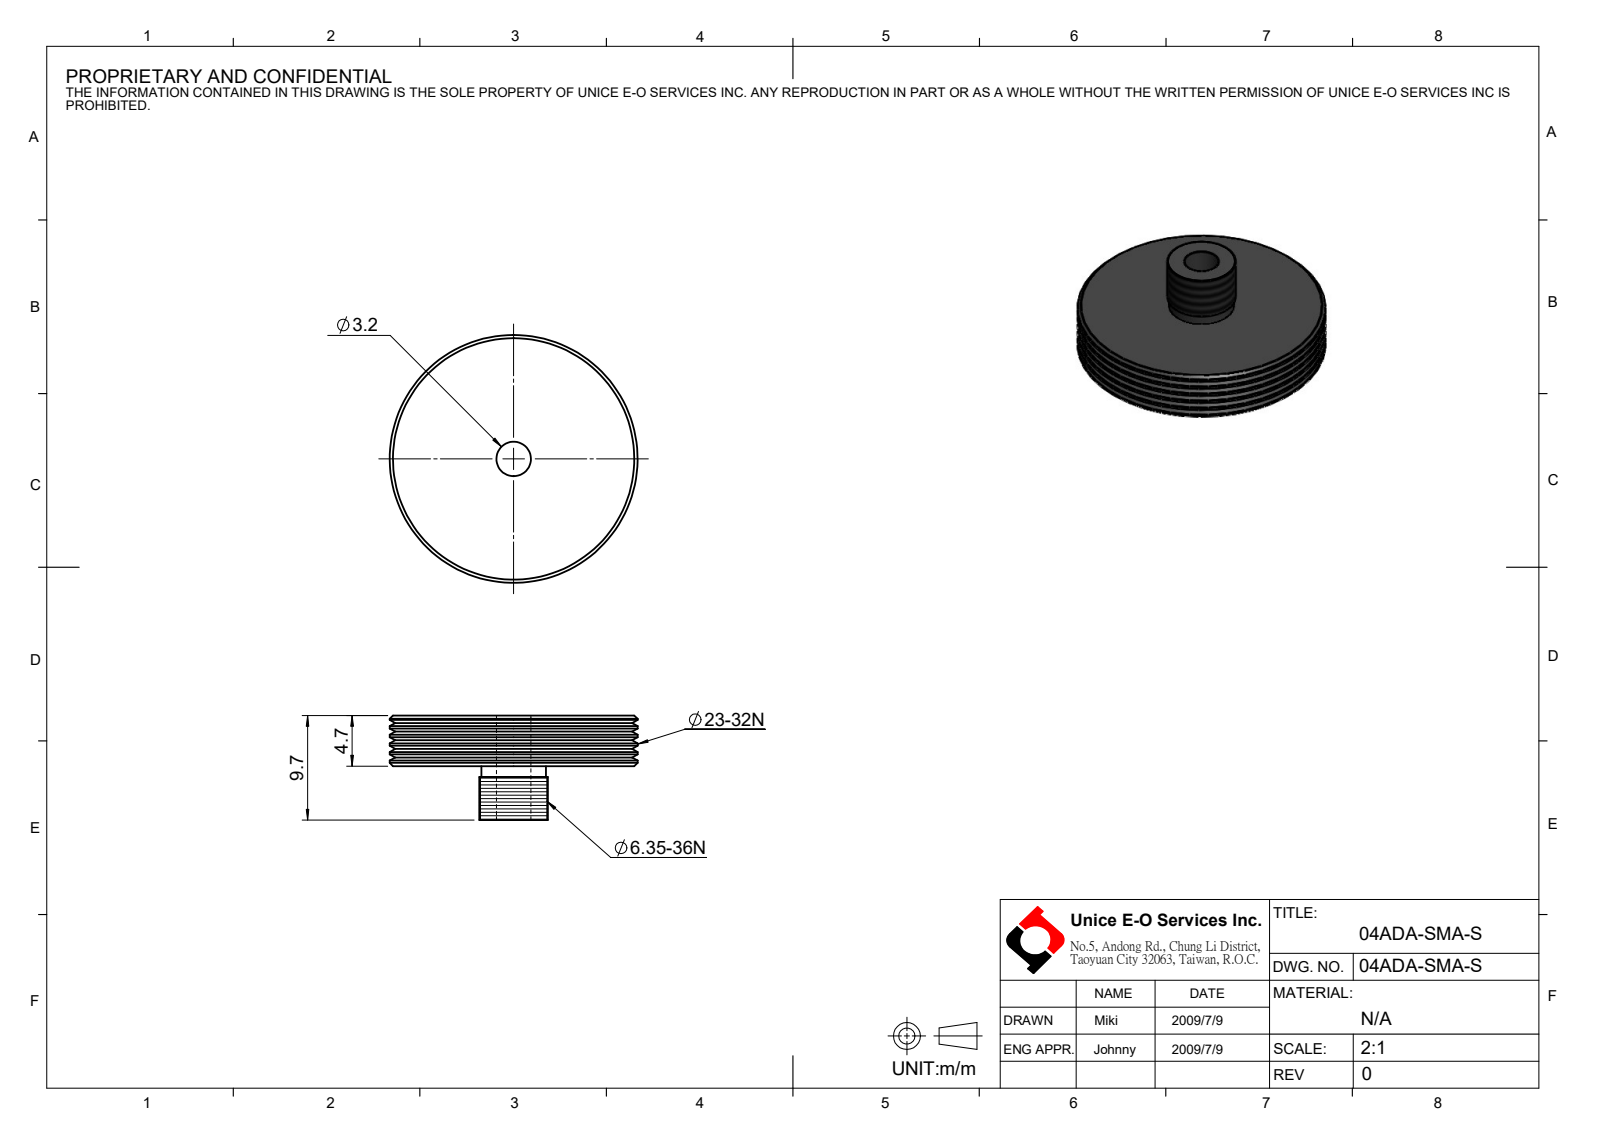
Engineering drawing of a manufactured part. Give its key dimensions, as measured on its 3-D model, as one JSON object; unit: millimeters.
{"part_name": "04ADA-SMA-S", "step_written_by": "SolidWorks 2016 (CONFIG_CONTROL_DESIGN)", "units": "millimeters", "bodies": {"solids": 1, "faces": 46, "planar": 4, "cylindrical": 18, "other": 24}, "overall_size": [23, 23, 9.7], "volume_mm3": 1972, "surface_area_mm2": 1531, "round_holes": [[3.2, 1]], "round_bosses_or_shafts": [[23, 1], [6.35, 1], [6, 1]], "face_to_face_distances": [4.7, 9.7, 5, 5.7, 1, 4]}
